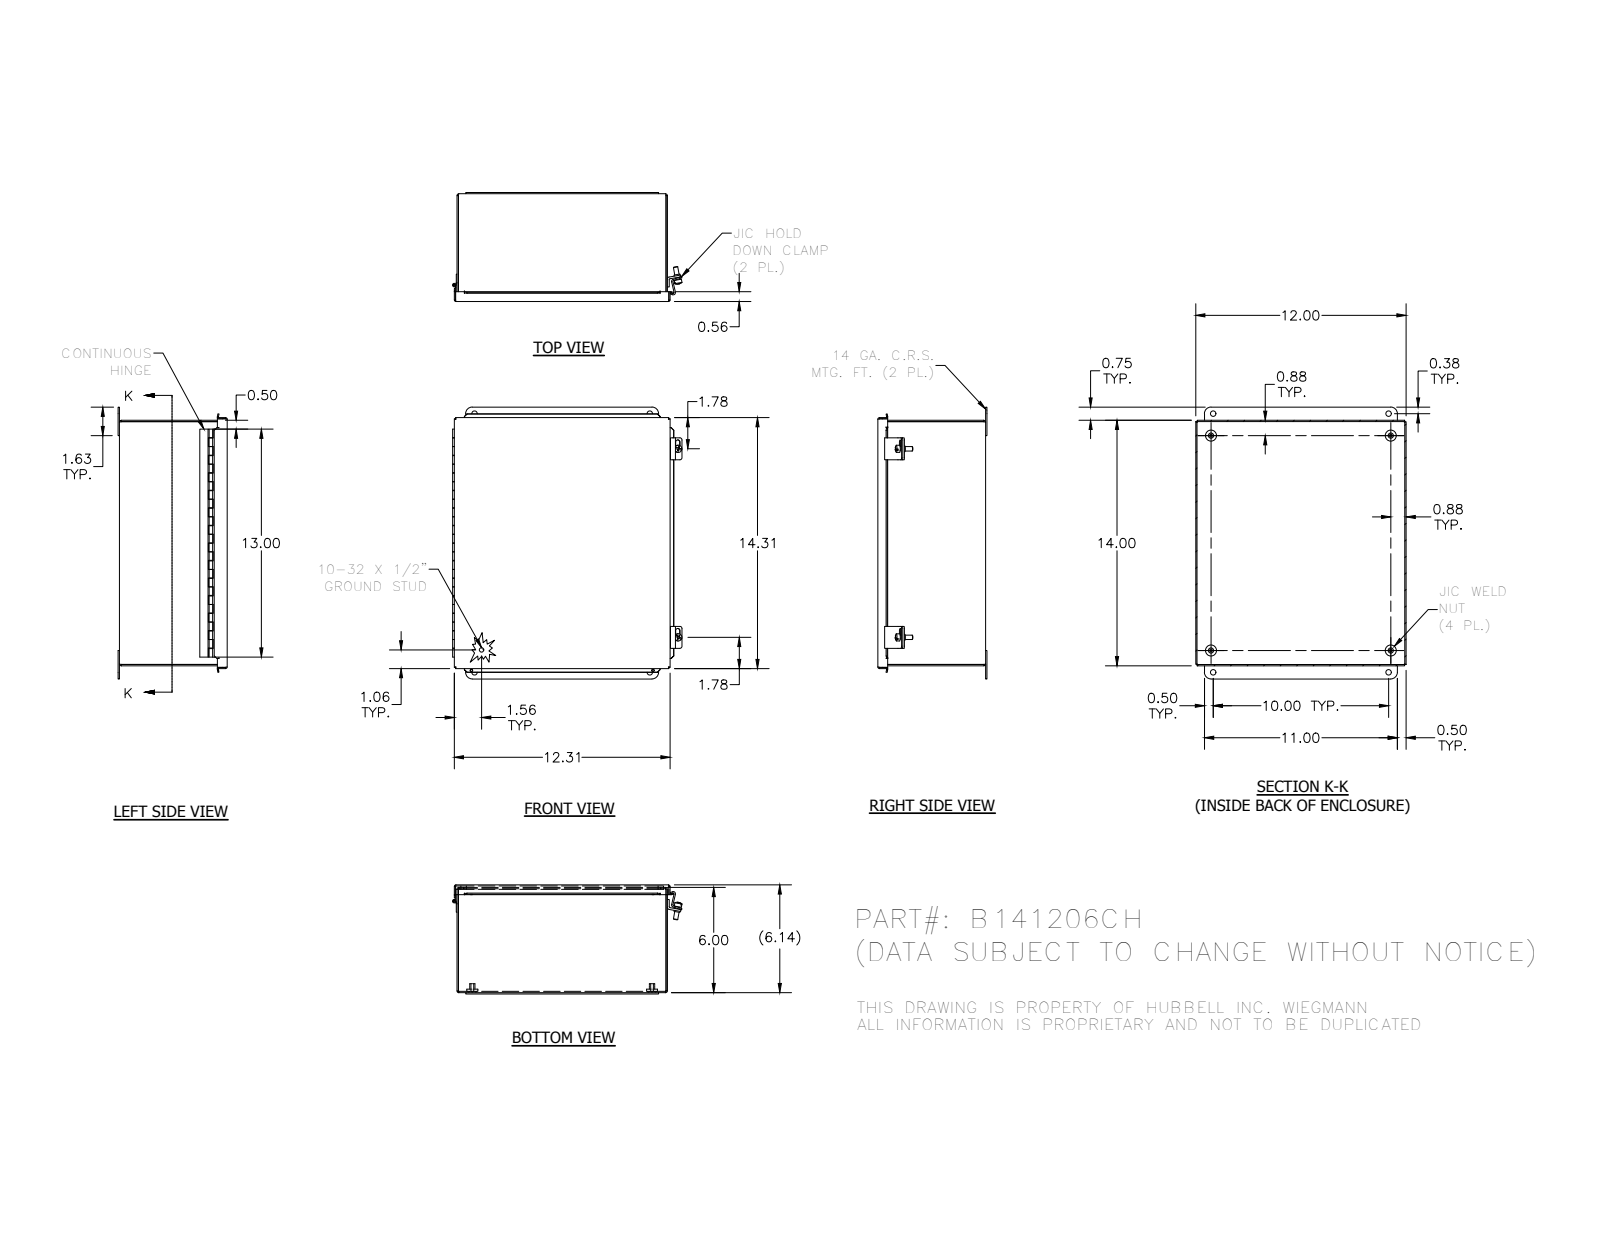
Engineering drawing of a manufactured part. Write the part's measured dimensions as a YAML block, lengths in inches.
part_name: "B141206CH; 3499; 3485; C1001 (+8 more)"
step_written_by: "Autodesk Inventor 2012 (AUTOMOTIVE_DESIGN)"
units: inches
bodies: {solids: 20, faces: 519, planar: 335, cylindrical: 139, other: 45}
overall_size: [15.5, 13.087, 6.219]
volume: 59.42
surface_area: 1634
round_holes:
  - {diameter: 0.156, count: 4}
  - {diameter: 0.31, count: 4}
  - {diameter: 0.14, count: 2}
  - {diameter: 0.196, count: 2}
  - {diameter: 0.116, count: 1}
round_bosses_or_shafts:
  - {diameter: 0.625, count: 4}
  - {diameter: 0.3, count: 4}
  - {diameter: 0.25, count: 3}
  - {diameter: 0.41, count: 2}
  - {diameter: 0.344, count: 2}
  - {diameter: 0.2, count: 1}
  - {diameter: 0.19, count: 1}
  - {diameter: 0.1, count: 1}
partial_cylinders:
  - {radius: 0.031, count: 15}
  - {radius: 0.105, count: 8}
  - {radius: 0.125, count: 8}
  - {radius: 0.093, count: 7}
  - {radius: 0.133, count: 4}
  - {radius: 0.375, count: 4}
  - {radius: 0.063, count: 3}
  - {radius: 0.126, count: 3}
face_to_face_distances: [0.074, 6.083, 0.062, 6.144, 6.009, 6.07, 11.926, 13.926, 12, 11.852]
hole_center_spacings: [1.256, 10, 10.202, 10.202, 10.25, 13.501, 14.75, 16.875]
